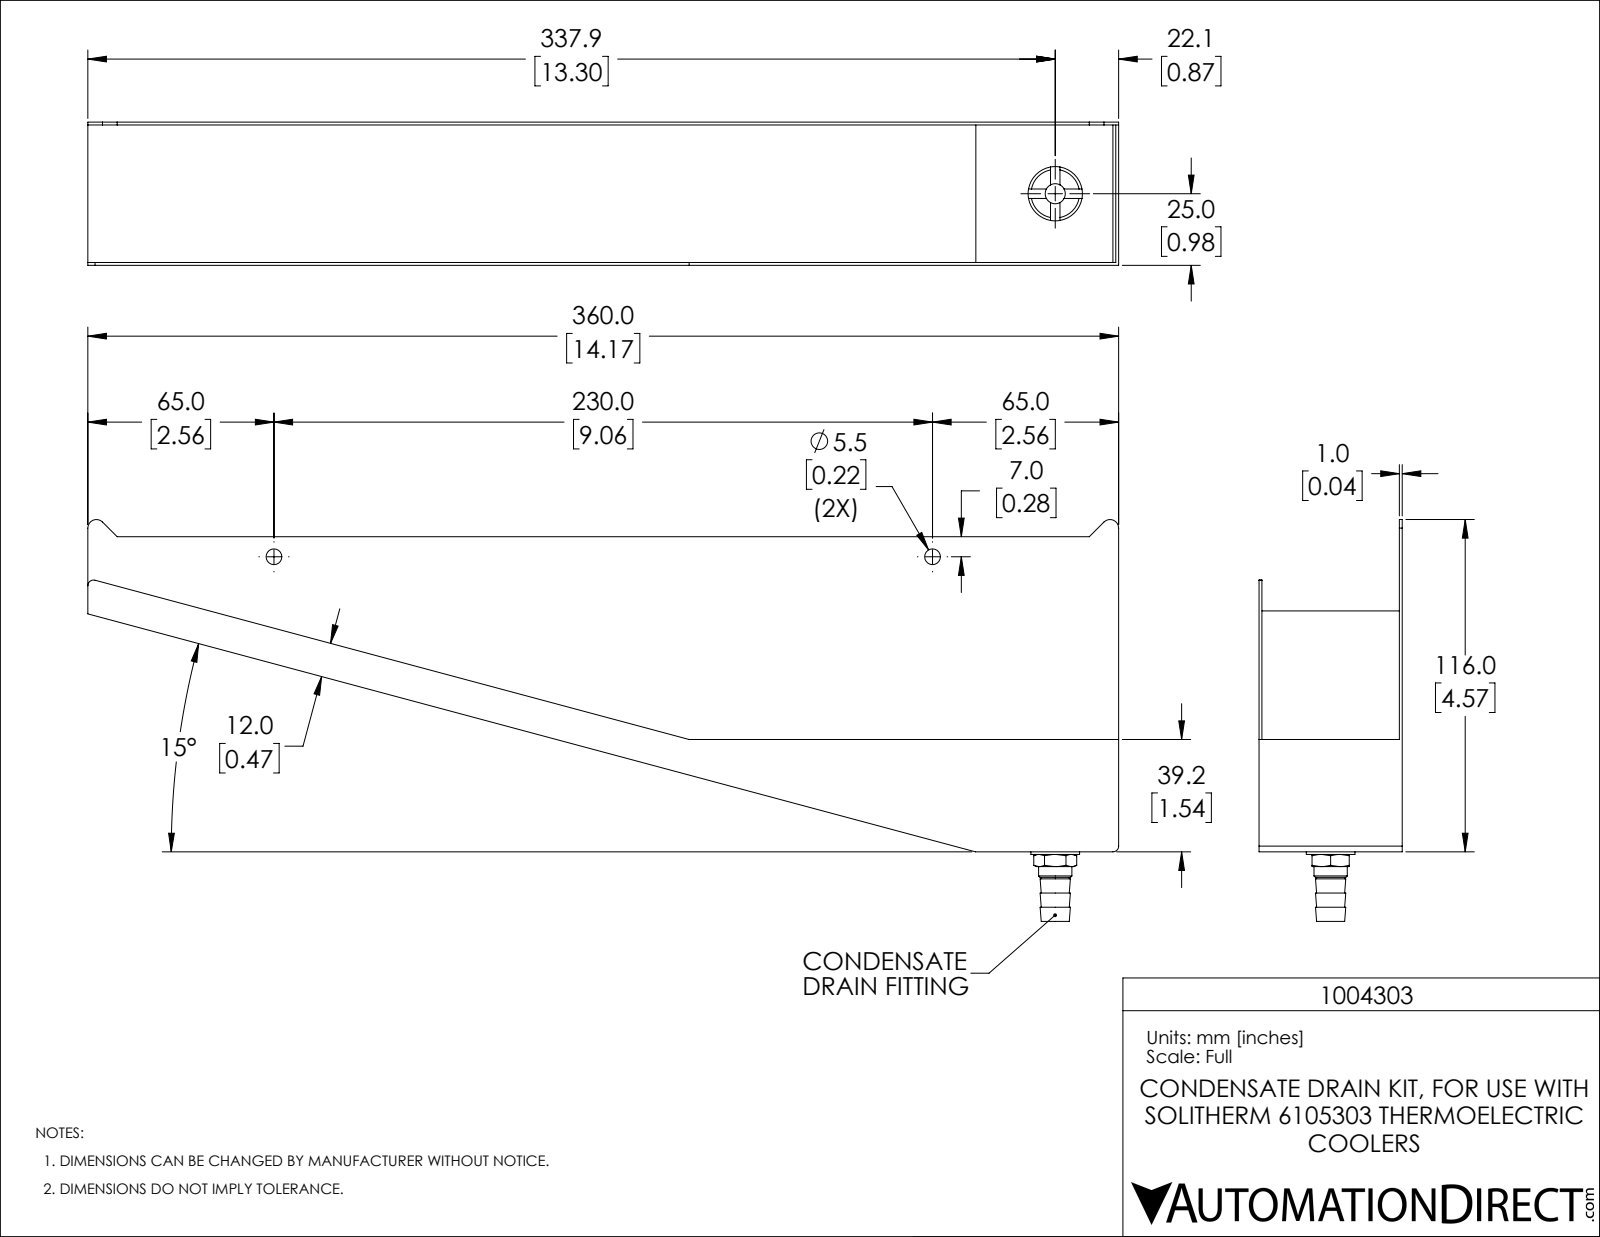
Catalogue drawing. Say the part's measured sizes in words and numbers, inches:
The part is named "1004303". Its 3-D file was written by "SolidWorks 2019 (AUTOMOTIVE_DESIGN)". It is 4 solids with 86 faces: 48 planar, 15 cylindrical and 23 other. Overall it measures 14.174 by 5.523 by 1.969 inches. Its volume is 3.39 cubic inches and its surface area 171.7 square inches. Round holes: 2 of diameter 0.217, 1 of diameter 0.276, 1 of diameter 0.394, 1 of diameter 0.433, 1 of diameter 0.484. Round bosses or shafts: 1 of diameter 0.746, 1 of diameter 0.669, 1 of diameter 0.457, 1 of diameter 0.387. Partial cylindrical surfaces (rounded edges, fillets, slot ends): 2 of radius 0.079, 2 of radius 0.118, 1 of radius 0.039. The main face-to-face distances are 0.039, 1.929, 1.969, 1.89, 4.331, 4.291, 0.435, 0.475, 1.544, 1.505. The hole center spacings are 9.055.
